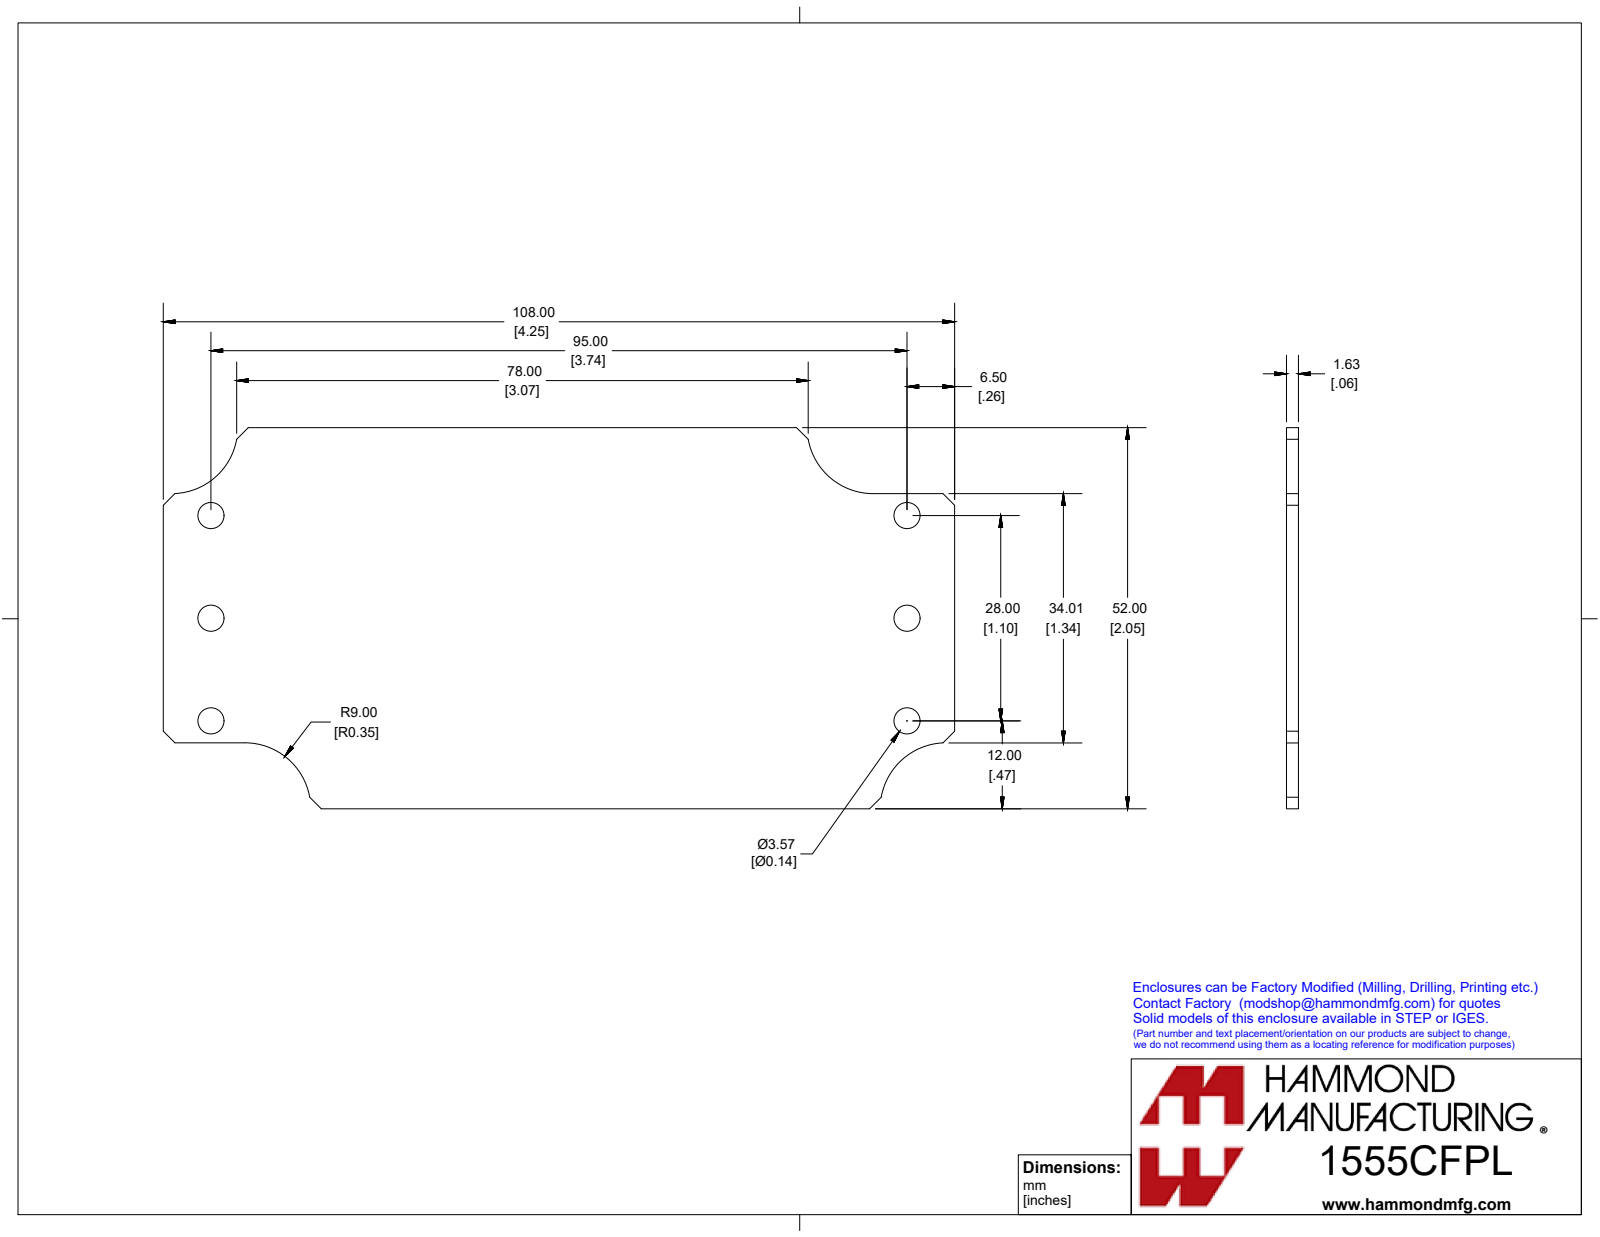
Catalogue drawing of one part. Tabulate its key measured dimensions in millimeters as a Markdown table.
| quantity | value |
| --- | --- |
| part name | 1555CFPL |
| STEP written by | SolidWorks 2019 (CONFIG_CONTROL_DESIGN) |
| units | millimeters |
| bodies | 1 solid, 26 faces (16 planar, 10 cylindrical, 0 other) |
| overall size | 108 × 52 × 1.6 |
| volume | 8 280 mm³ |
| surface area | 10 750 mm² |
| round holes (diameter × count) | 3 × 6 |
| partial cylindrical surfaces (radius × count) | 9 × 4 |
| main face-to-face distances | 1.6, 52, 108, 9, 43, 34, 98.1, 0.7, 97.4, 7.8 |
| hole center spacings | 14, 96, 95, 28, 99 |
